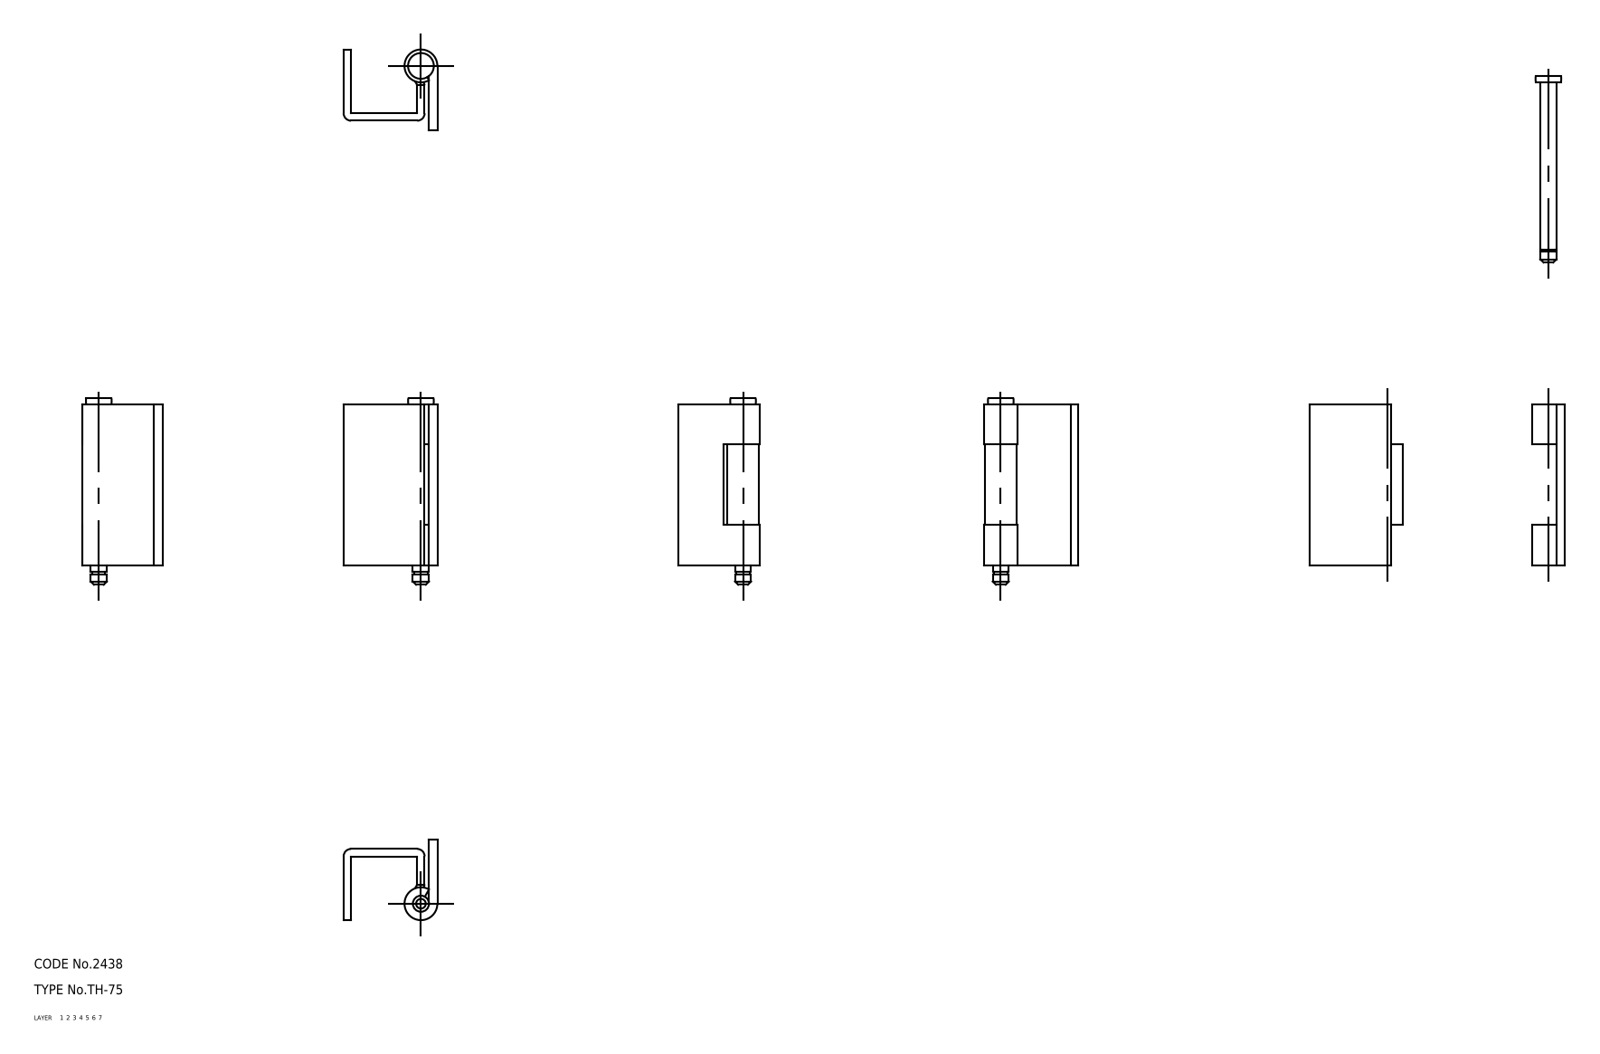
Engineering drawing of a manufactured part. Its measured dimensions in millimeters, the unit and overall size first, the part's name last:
Units: millimetres
Overall size (bounding box): 58 × 29.1 × 25.1
Volume: 12 302 mm³ · Surface area: 11 411 mm²
Bodies: 3 solids, 48 faces (0 planar, 0 cylindrical, 48 other)
Part name (STEP PRODUCT): shaft; hinge piece_B; hinge piece_A; TH_75_14600_36
STEP written by: CADfix (AUTOMOTIVE_DESIGN)
